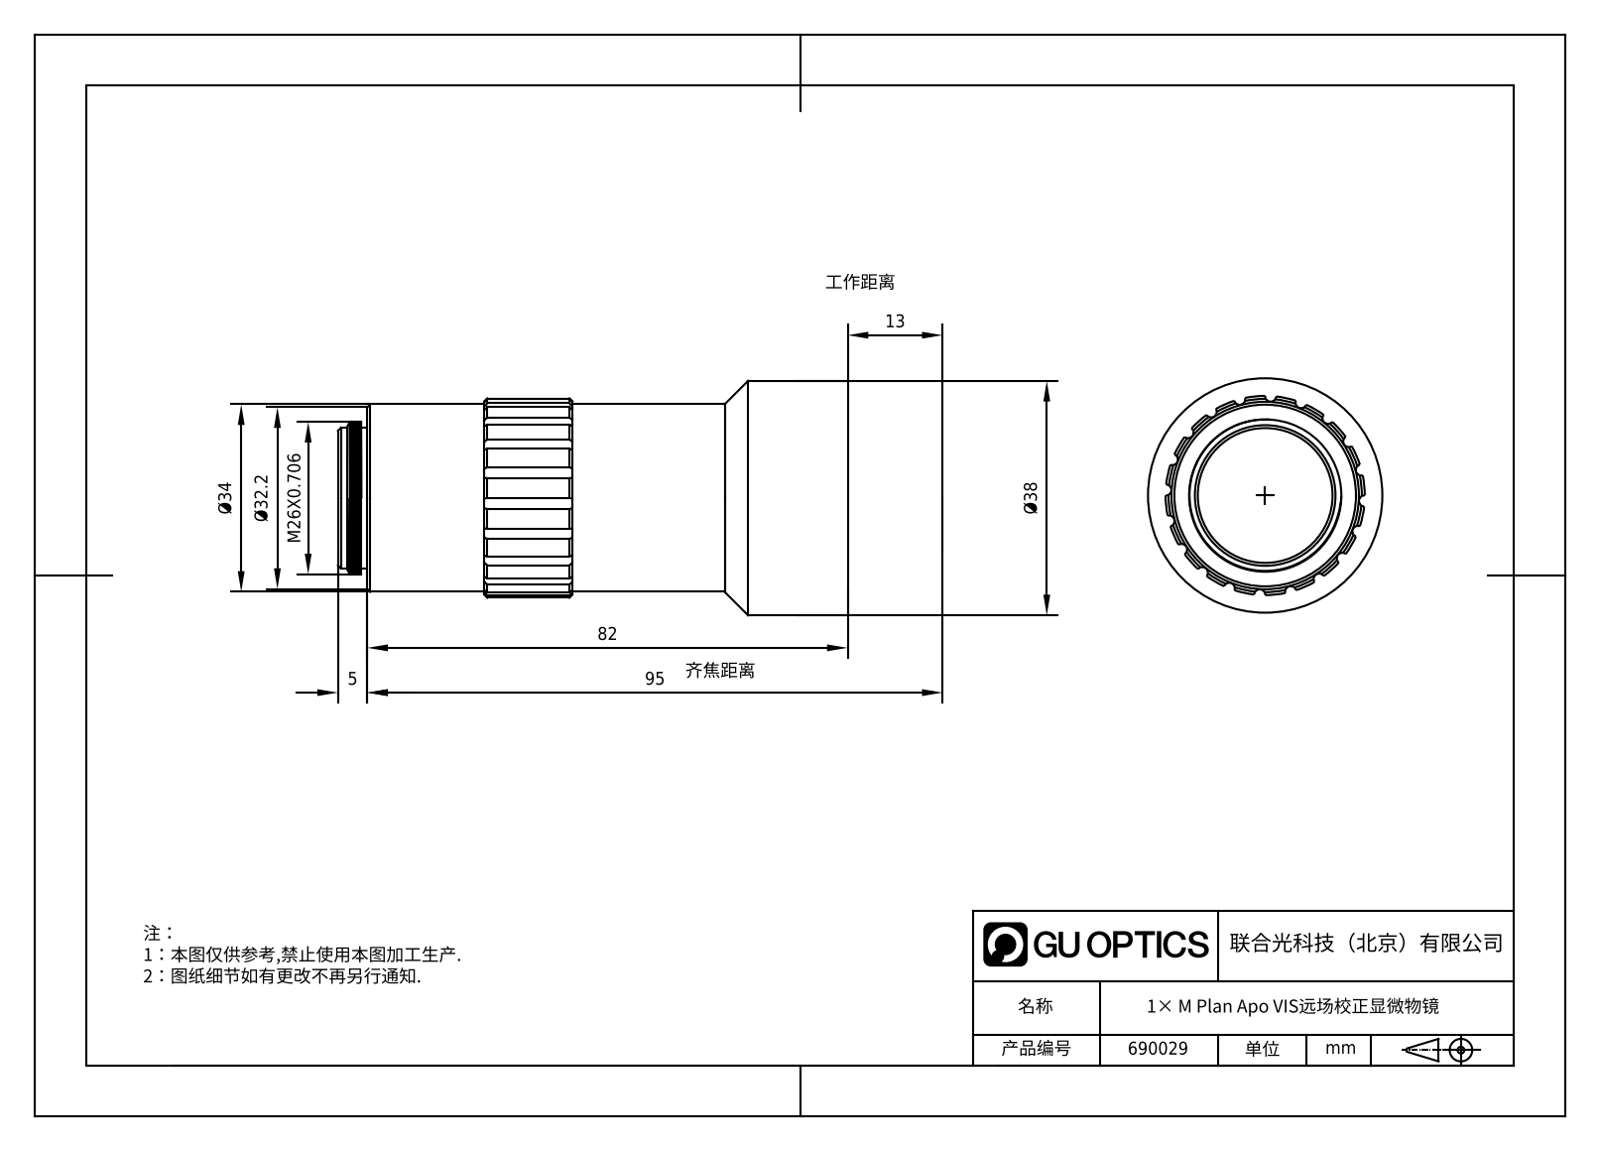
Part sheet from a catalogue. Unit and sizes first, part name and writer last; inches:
Units: inches
Overall size (bounding box): 3.425 × 1.575 × 1.575
Round holes (diameter × count): ⌀1.417 ×1, ⌀1.496 ×1
Round bosses / shafts (diameter × count): ⌀1.575 ×1, ⌀1.496 ×1, ⌀1.26 ×1, ⌀1.024 ×1, ⌀0.945 ×1
Partial cylindrical surfaces — rounded edges, fillets, slot ends (radius × count): R0.037 ×20, R0.63 ×1, R0.669 ×1
Main face-to-face distances: 0.748, 3.346, 2.598, 3.15, 2.402, 0.197, 0.827, 0.079, 3.228, 3.425
Volume: 4.637 in³ · Surface area: 22.65 in²
Bodies: 4 solids, 366 faces (146 planar, 88 cylindrical, 132 other)
Part name (STEP PRODUCT): 690029
STEP written by: SolidWorks 2020 (AUTOMOTIVE_DESIGN)
